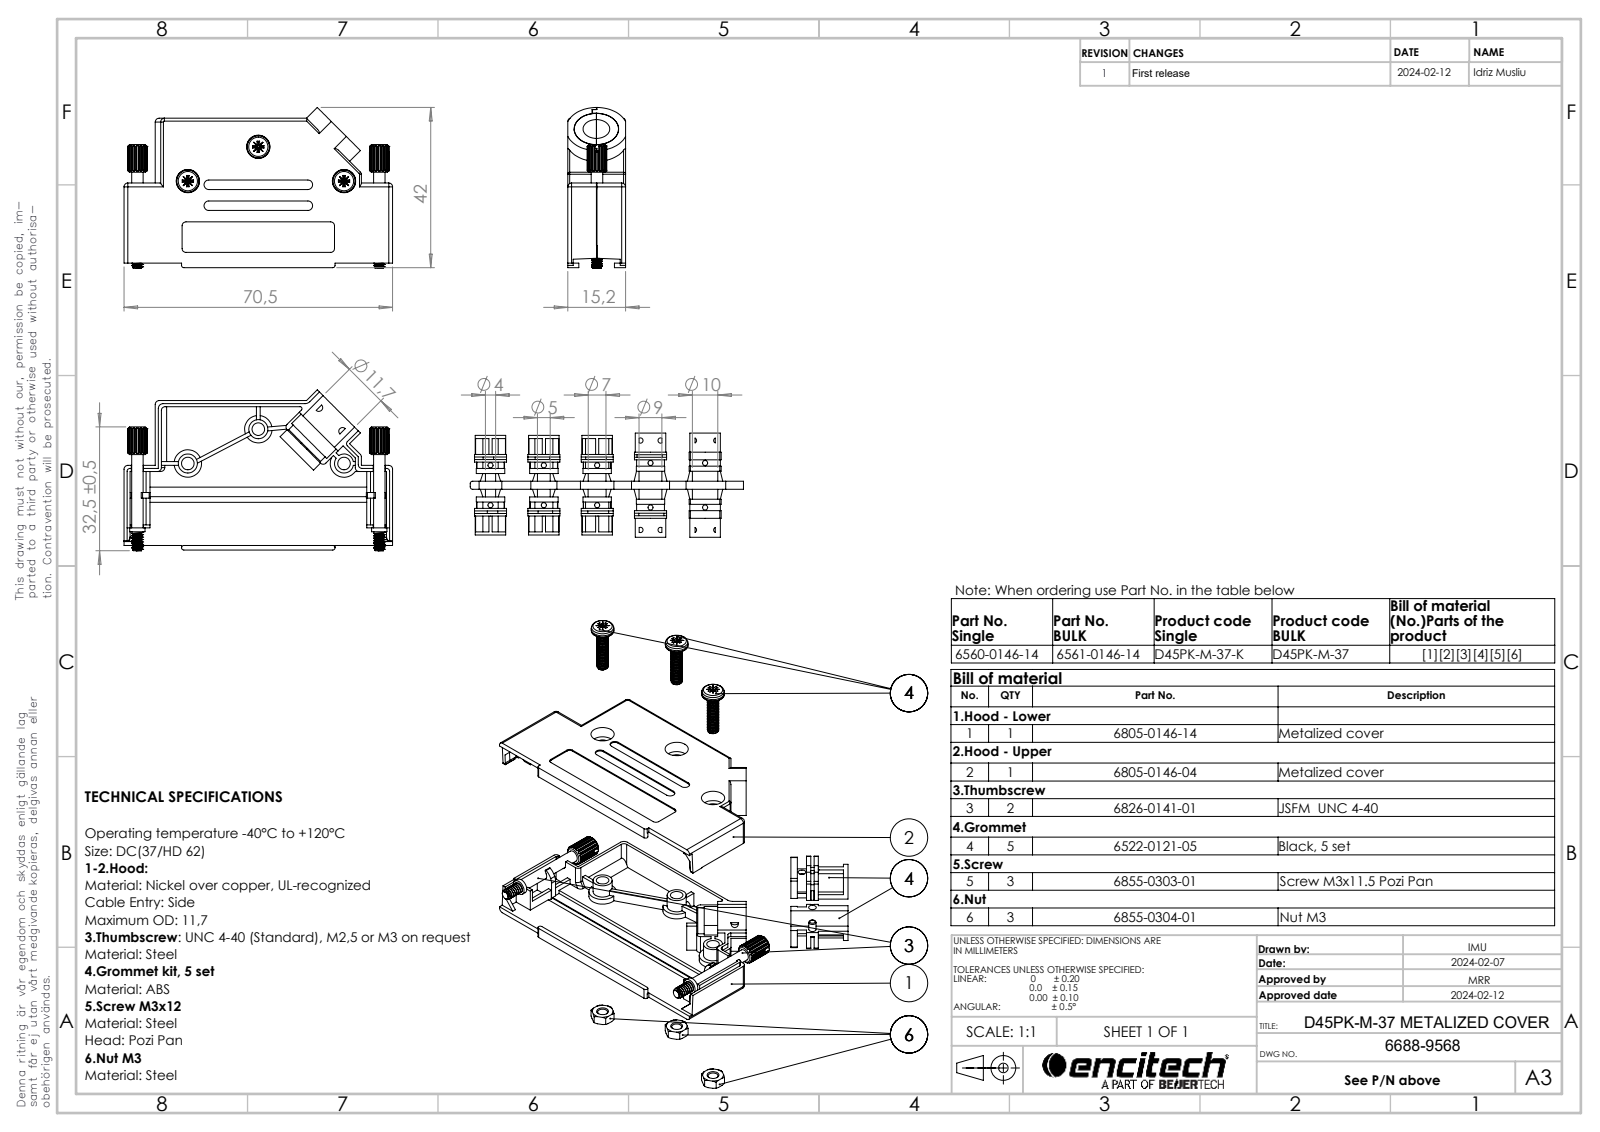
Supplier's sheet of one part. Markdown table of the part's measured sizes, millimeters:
| quantity | value |
| --- | --- |
| part name | 6826-0141-01; 6855-0303-01; 6522-0121-05 (7mm); 6805-0146-14 (+3 more) |
| STEP written by | SolidWorks 2021 (AUTOMOTIVE_DESIGN) |
| units | millimeters |
| bodies | 12 solids, 1083 faces (650 planar, 285 cylindrical, 148 other) |
| overall size | 70.5 × 42.23 × 15.15 |
| volume | 12 939 mm³ |
| surface area | 19 627 mm² |
| round holes (diameter × count) | 2 × 3, 2.6 × 3, 3.3 × 3, 6.1 × 3, 7 × 1, 11.7 × 1 |
| round bosses / shafts (diameter × count) | 5 × 3, 2.9 × 3, 7.2 × 2, 4 × 2, 3 × 2, 2.8 × 2, 1.9 × 2, 11.6 × 1 |
| partial cylindrical surfaces (radius × count) | 1 × 26, 0.5 × 13, 0.1 × 12, 0.75 × 8, 1.25 × 5, 1.6 × 4, 5.64 × 4, 5.91 × 4 |
| main face-to-face distances | 1.4, 13.75, 15.15, 12.35, 1, 1.6, 1.1, 2.4, 2.1, 14.85 |
| hole center spacings | 5.71, 5.67, 10.01, 11.11, 11.16, 13.16, 15.65, 18.87 |
